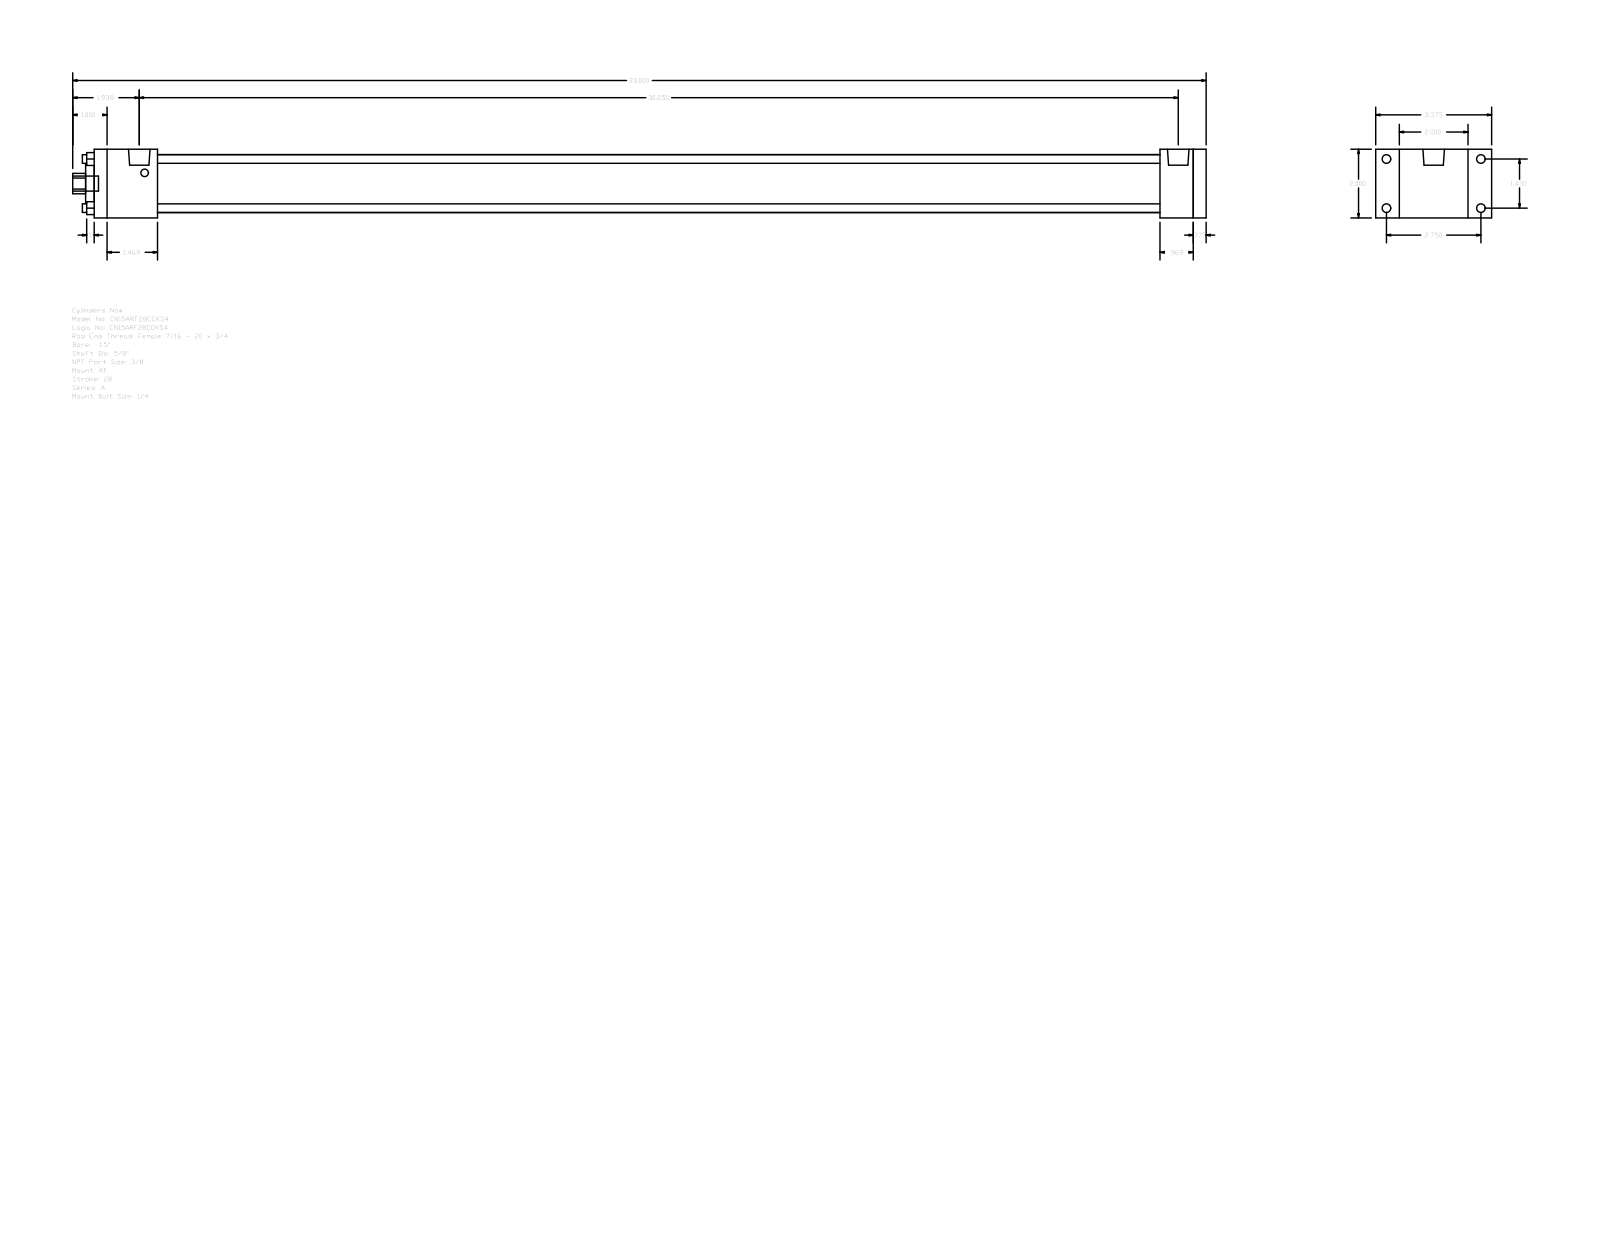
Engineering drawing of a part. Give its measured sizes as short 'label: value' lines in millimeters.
name: A_RF__0150_0.625
written by: GSSL Pune (CONFIG_CONTROL_DESIGN)
unit: mm
bodies: 0 solids, 92 faces (64 planar, 28 cylindrical, 0 other)
size: 838.2 × 85.72 × 50.8
holes: 4× ⌀6.35, 1× ⌀15.88, 1× ⌀28.57, 1× ⌀42.93
bosses: 4× ⌀6.35, 4× ⌀5.56, 2× ⌀15.93, 1× ⌀11.11
rounds: 1× R7.54
face distances: 50.8, 9.53, 822.32, 812.79, 788.19, 24.6, 34.13, 46.83, 741.36, 765.96
hole spacings: 25.68, 36.32, 51.36
